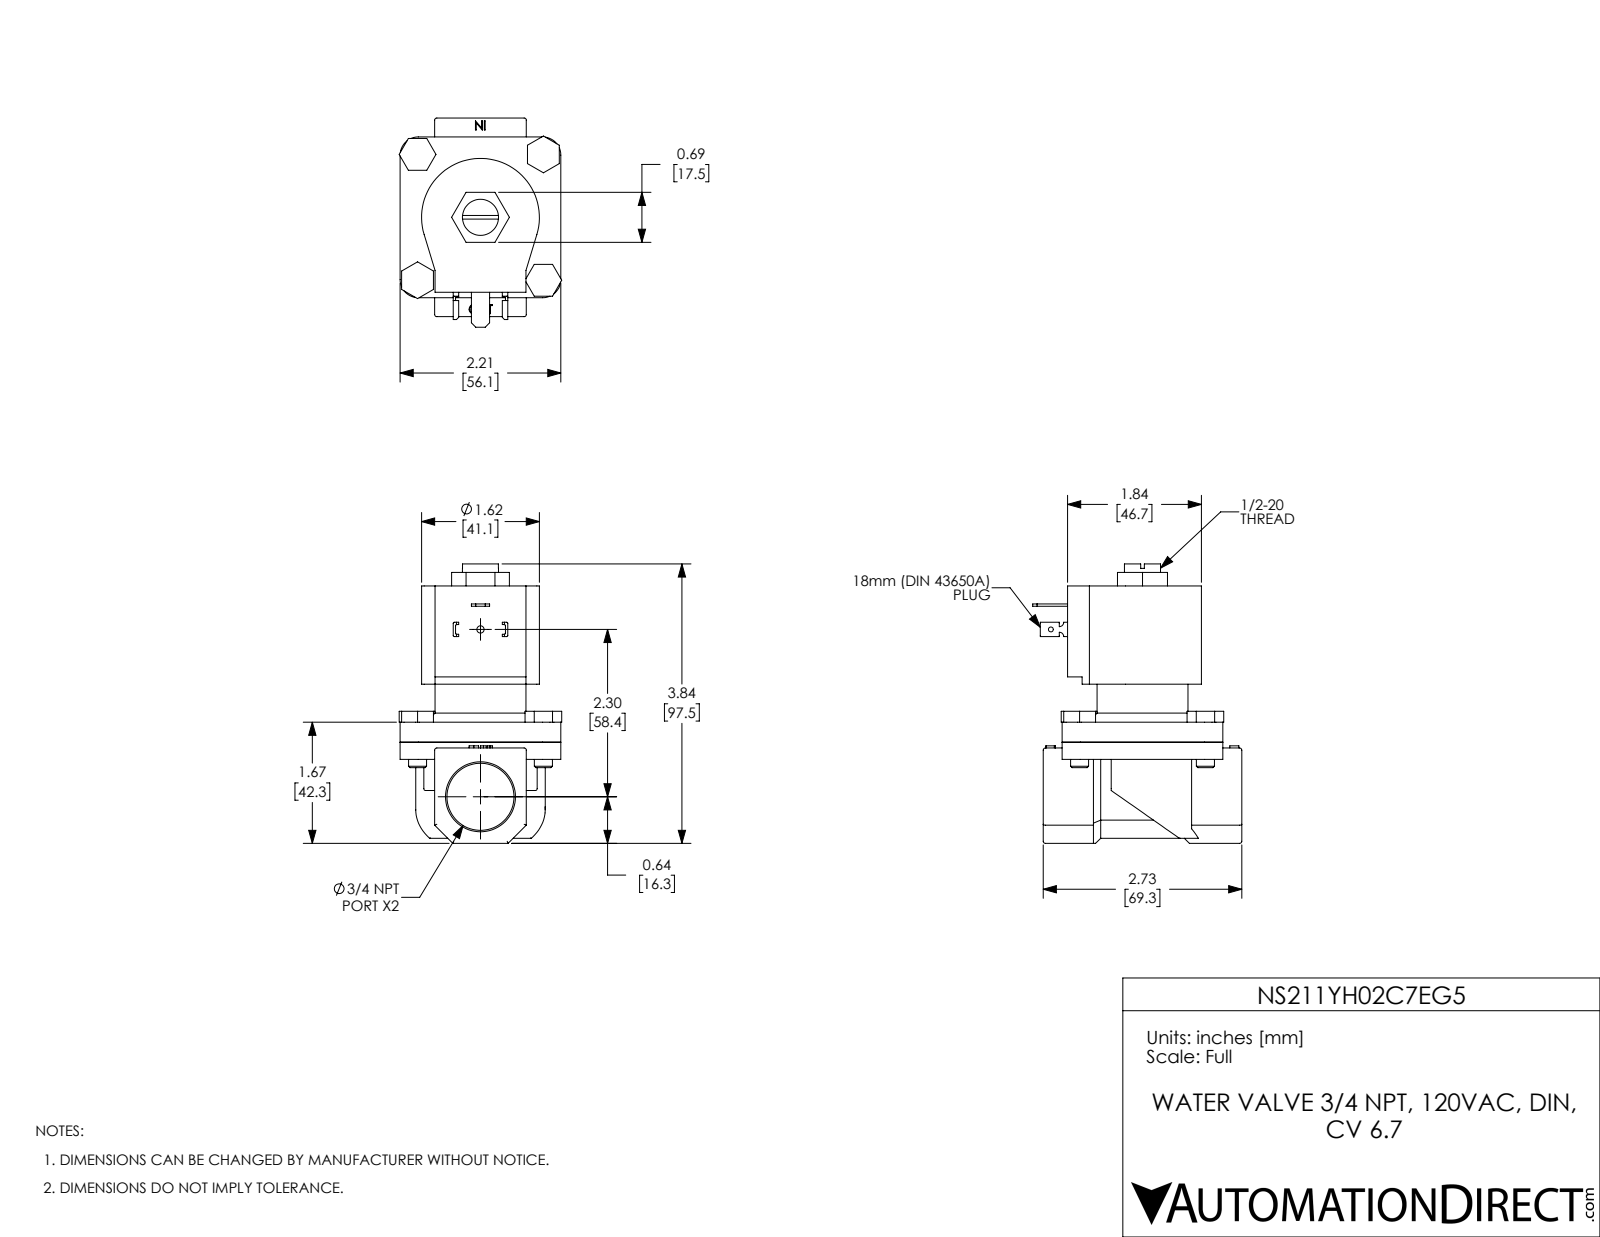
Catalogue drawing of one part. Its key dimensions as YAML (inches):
part_name: "NS211YH02C7EG5"
step_written_by: "SolidWorks 2024 (CONFIG_CONTROL_DESIGN)"
units: inches
bodies: {solids: 11, faces: 332, planar: 198, cylindrical: 99, other: 35}
overall_size: [3.84, 2.875, 2.235]
volume: 9.853
surface_area: 64.15
round_holes:
  - {diameter: 0.25, count: 4}
  - {diameter: 0.067, count: 1}
  - {diameter: 0.1, count: 1}
  - {diameter: 0.496, count: 1}
  - {diameter: 0.512, count: 1}
  - {diameter: 0.922, count: 1}
  - {diameter: 1.155, count: 1}
round_bosses_or_shafts:
  - {diameter: 0.248, count: 4}
  - {diameter: 1.25, count: 1}
partial_cylinders:
  - {radius: 0.03, count: 15}
  - {radius: 0.015, count: 8}
  - {radius: 0.25, count: 4}
  - {radius: 0.06, count: 2}
  - {radius: 0.81, count: 1}
  - {radius: 0.89, count: 1}
face_to_face_distances: [0.275, 2.148, 1.873, 0.475, 1.735, 2.21, 0.798, 0.523, 1.35, 0.236]
hole_center_spacings: [1.223, 1.73, 2.446, 2.3]
